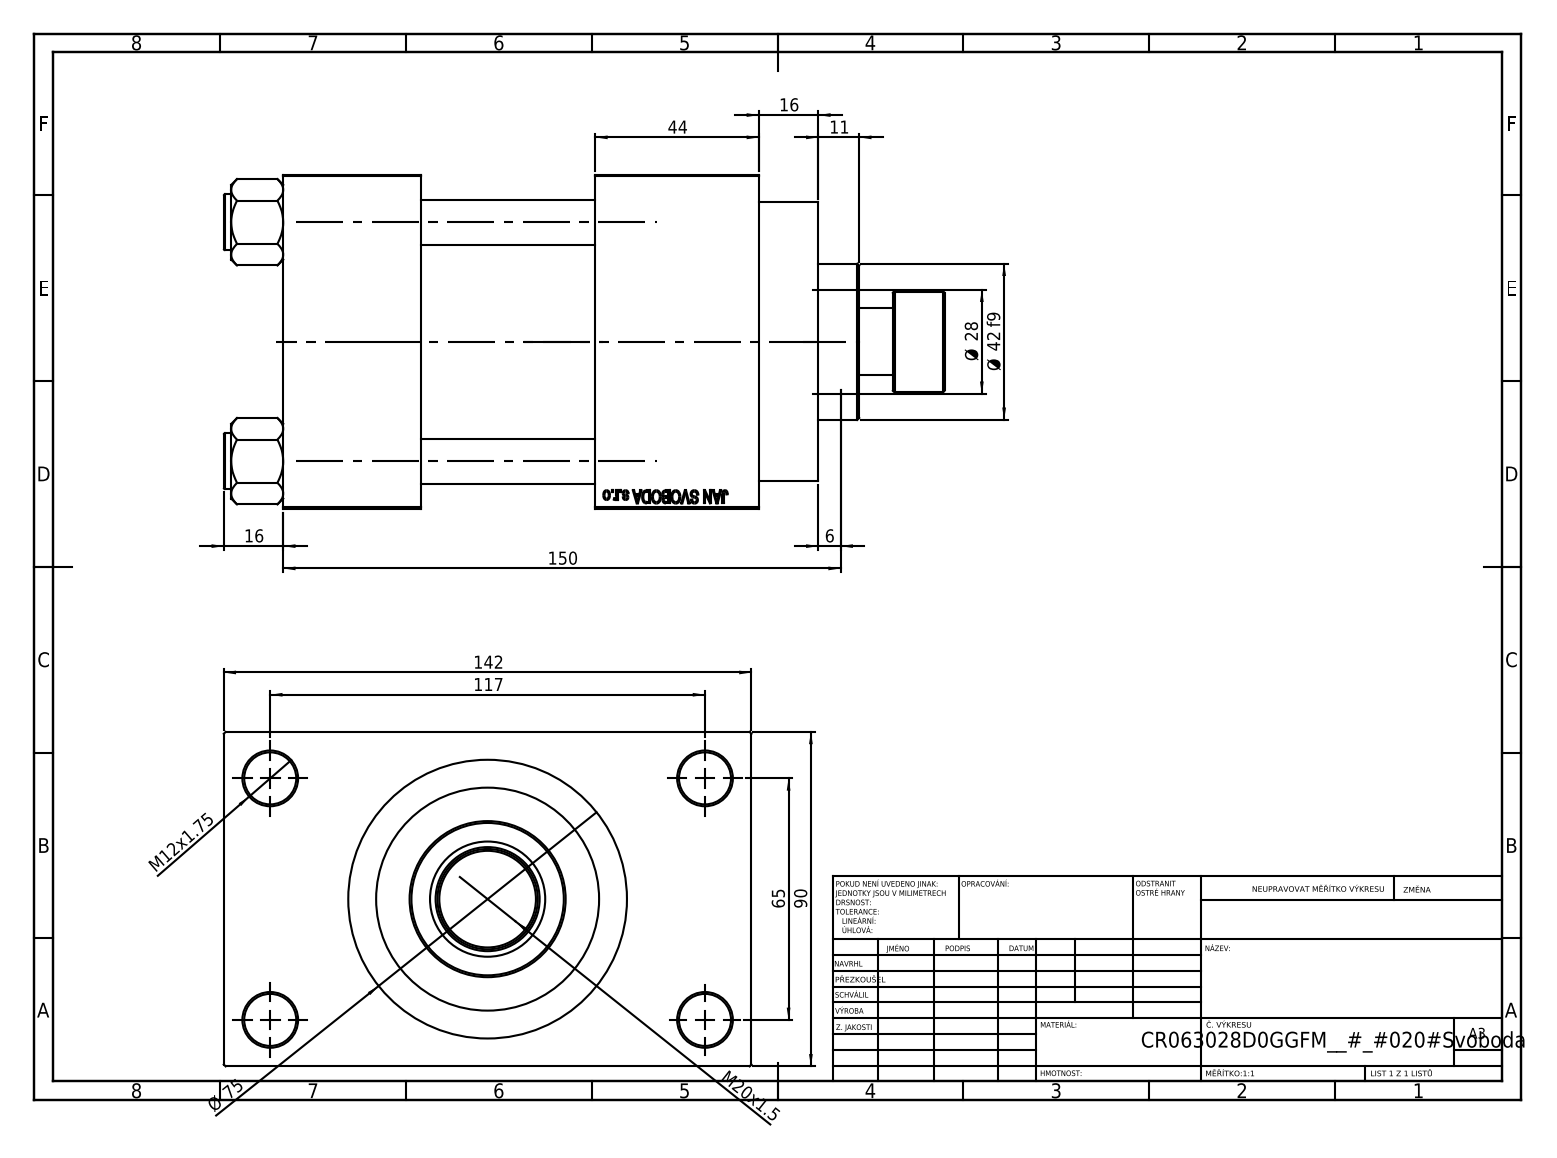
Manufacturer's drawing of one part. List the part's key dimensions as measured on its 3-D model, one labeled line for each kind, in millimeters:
Part name (STEP PRODUCT): V215CR_ROD_END_F; V215_VC_A; V215CR_D_Body; V215CR_D_TYCINKA (+2 more)
STEP written by: SolidWorks 2019 (CONFIG_CONTROL_DESIGN)
Units: millimetres
Bodies: 12 solids, 1118 faces (501 planar, 93 cylindrical, 524 other)
Overall size (bounding box): 194 × 142 × 90
Volume: 1 042 000 mm³ · Surface area: 187 940 mm²
Round holes (diameter × count): ⌀12 ×4, ⌀14 ×4, ⌀7 ×2, ⌀20.96 ×2, ⌀30 ×2, ⌀18.5 ×1, ⌀28 ×1, ⌀31 ×1, ⌀50 ×1, ⌀60 ×1, ⌀63 ×1
Round bosses / shafts (diameter × count): ⌀15 ×4, ⌀75 ×1, ⌀69 ×1, ⌀42 ×1, ⌀27 ×1, ⌀18 ×1
Main face-to-face distances: 90, 47, 37, 84, 91, 128, 44, 26, 116, 64
Hole centre spacings: 26.35, 45.47, 64.3, 66.92, 69.81, 90.65, 111.34, 65
